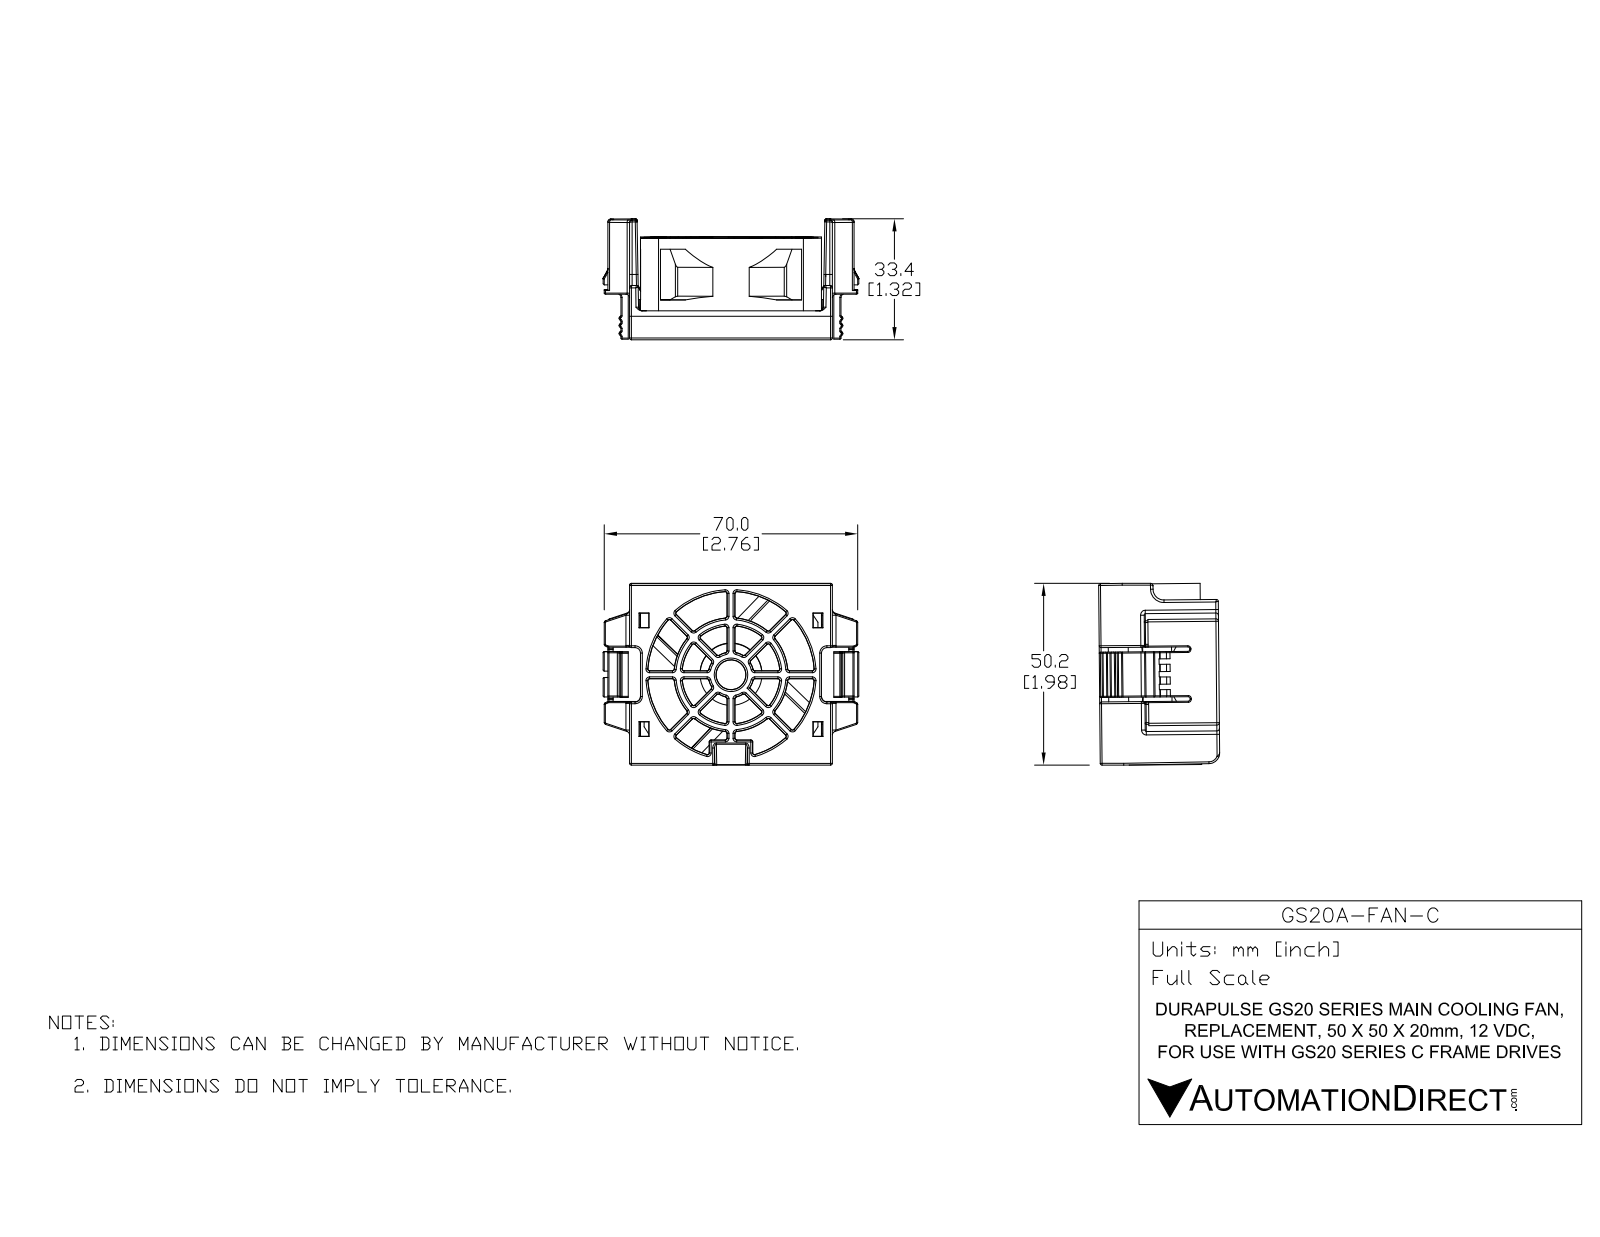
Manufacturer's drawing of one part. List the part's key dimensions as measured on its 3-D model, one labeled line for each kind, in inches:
Part name (STEP PRODUCT): GS20A-FAN-C
STEP written by: SolidWorks 2017 (AUTOMOTIVE_DESIGN)
Units: inches
Bodies: 2 solids, 1318 faces (421 planar, 382 cylindrical, 515 other)
Overall size (bounding box): 2.78 × 1.976 × 1.299
Volume: 1.498 in³ · Surface area: 41.93 in²
Round holes (diameter × count): ⌀0.177 ×4, ⌀1.087 ×1, ⌀1.89 ×1
Round bosses / shafts (diameter × count): ⌀1.165 ×1, ⌀0.674 ×1
Partial cylindrical surfaces — rounded edges, fillets, slot ends (radius × count): R0.02 ×103, R0.012 ×68, R0.039 ×24, R0.028 ×21, R0.059 ×5, R0.079 ×5, R0.128 ×4, R0.197 ×4
Main face-to-face distances: 0.098, 0.118, 1.102, 1.004, 2.087, 0.354, 2.323, 0.236, 1.969, 2.441
Hole centre spacings: 1.113, 1.575, 2.227
